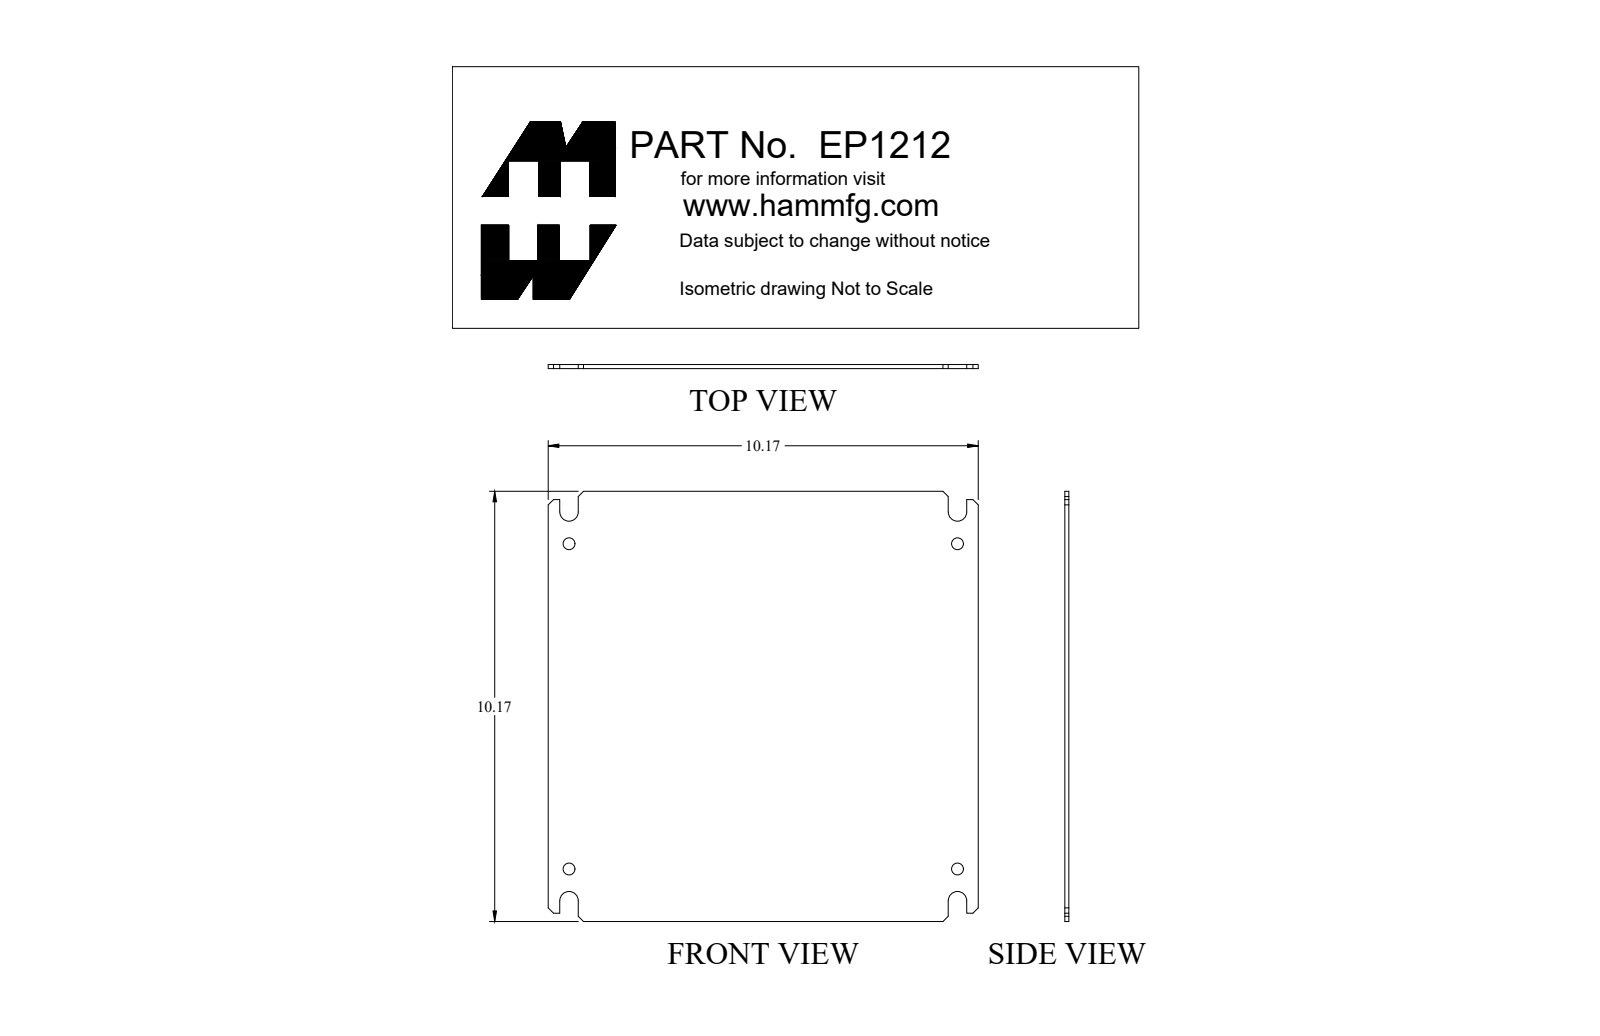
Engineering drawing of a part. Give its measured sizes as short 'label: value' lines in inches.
name: EP1212
written by: SolidWorks 2018 (AUTOMOTIVE_DESIGN)
unit: in
bodies: 1 solid, 40 faces (26 planar, 14 cylindrical, 0 other)
size: 10.17 × 10.17 × 0.095
volume: 9.666 in³; area: 208 in²
holes: 4× ⌀0.281
rounds: 4× R0.219
face distances: 0.095, 10.17, 0.709, 9.461, 0.272, 9.898, 0.437, 9.188, 8.751, 0.362
hole spacings: 7.688, 9.188, 11.98
